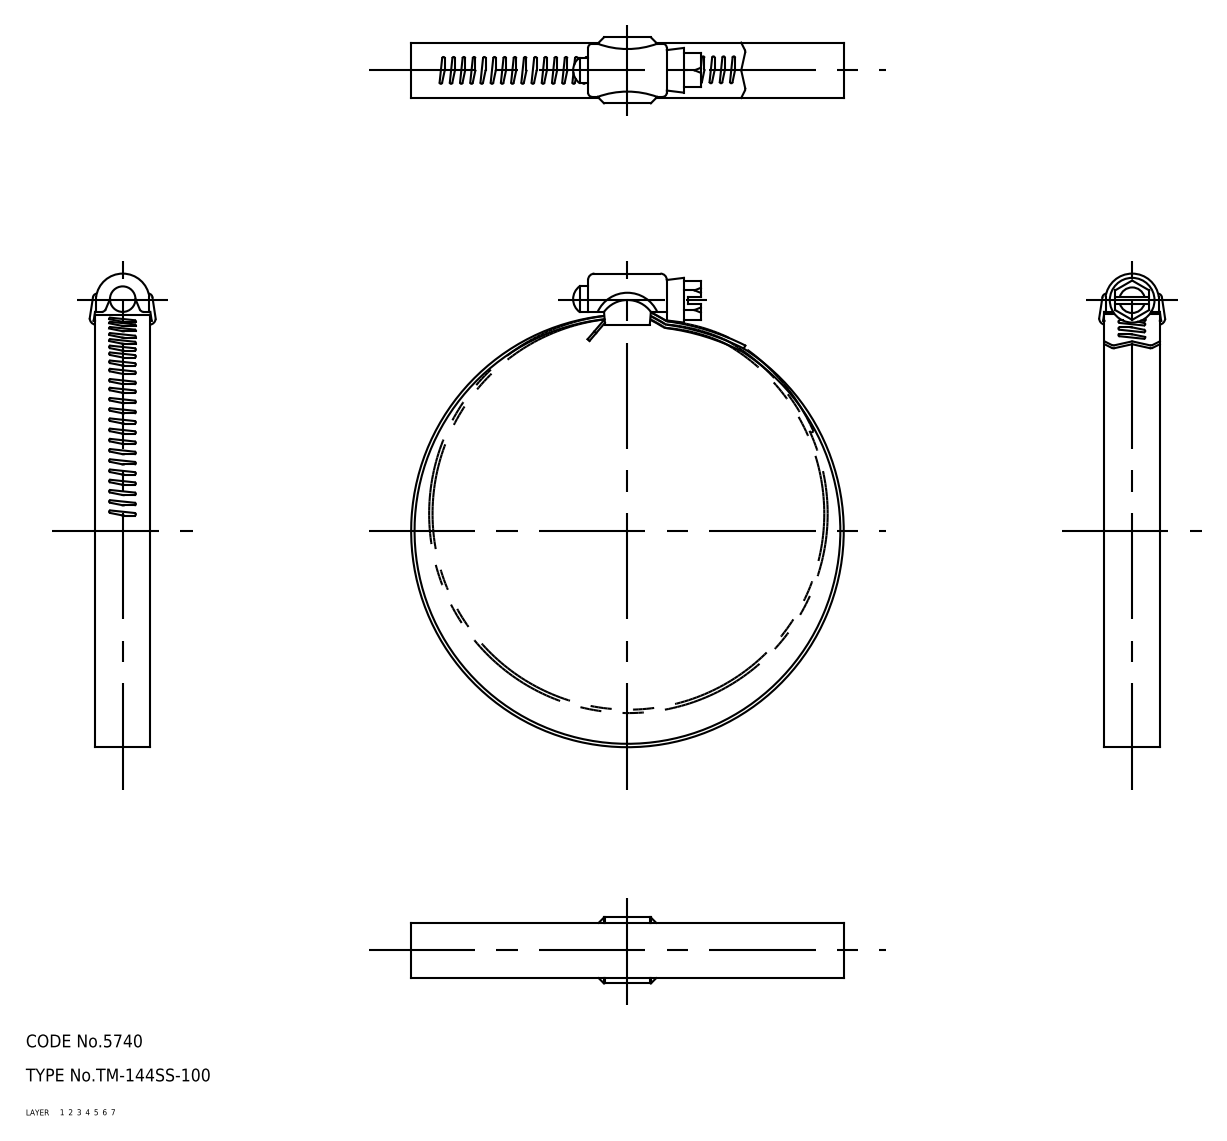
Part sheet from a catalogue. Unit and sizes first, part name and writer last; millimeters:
Units: millimetres
Overall size (bounding box): 111.23 × 101.6 × 15.63
Volume: 5 803 mm³ · Surface area: 12 039 mm²
Bodies: 3 solids, 216 faces (0 planar, 0 cylindrical, 216 other)
Part name (STEP PRODUCT): screw; holder; band; TM_144SS_100_19374_36
STEP written by: CADfix (AUTOMOTIVE_DESIGN)
